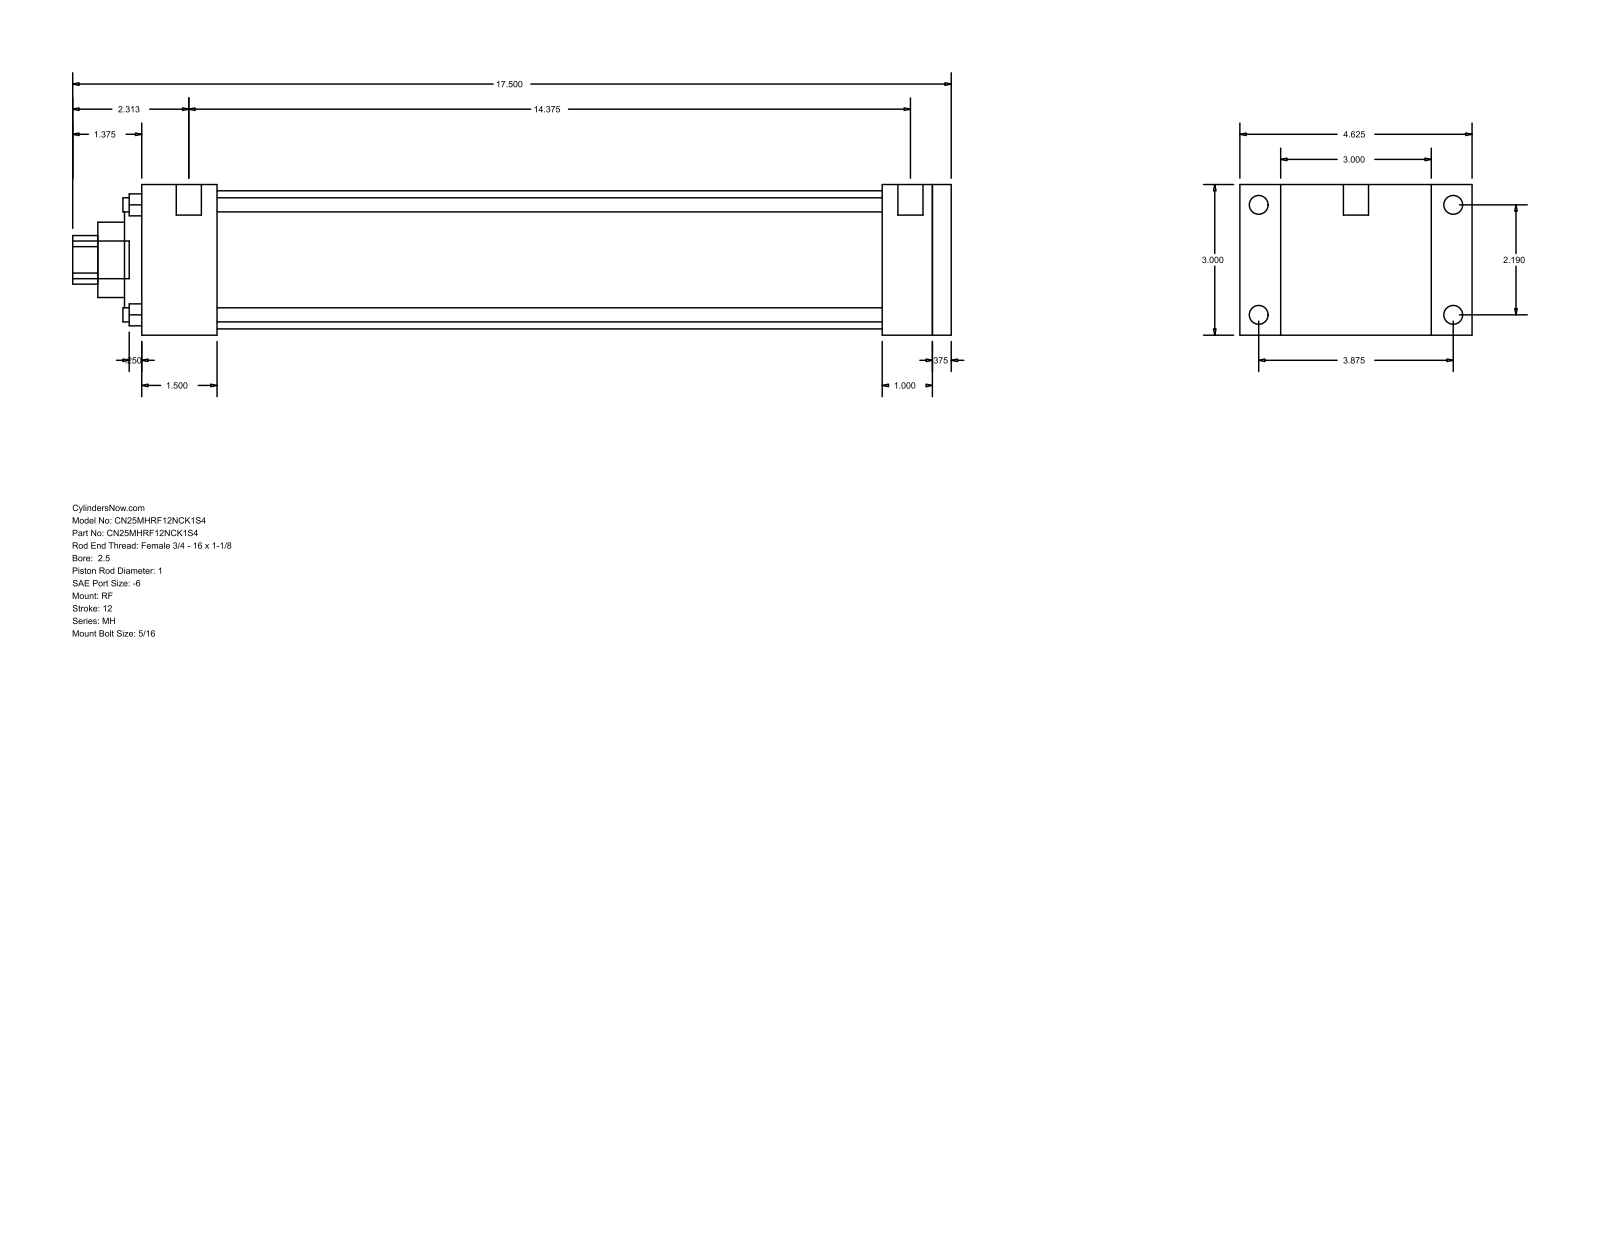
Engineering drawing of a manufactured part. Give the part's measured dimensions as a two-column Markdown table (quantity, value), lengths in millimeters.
| quantity | value |
| --- | --- |
| part name | MH_RF__0250_1 |
| STEP written by | GSSL Pune (CONFIG_CONTROL_DESIGN) |
| units | millimeters |
| bodies | 0 solids, 94 faces (65 planar, 29 cylindrical, 0 other) |
| overall size | 444.5 × 117.47 × 76.2 |
| round holes (diameter × count) | 7.14 × 4, 25.4 × 1, 38.1 × 1, 60.33 × 1, 69.85 × 1 |
| round bosses / shafts (diameter × count) | 9.53 × 4, 5.56 × 4, 12.7 × 2, 19.05 × 1 |
| partial cylindrical surfaces (radius × count) | 12.29 × 1 |
| main face-to-face distances | 76.2, 9.52, 409.58, 400.06, 374.65, 25.41, 34.93, 38.11, 336.54, 361.95 |
| hole center spacings | 39.33, 55.62, 78.66 |
